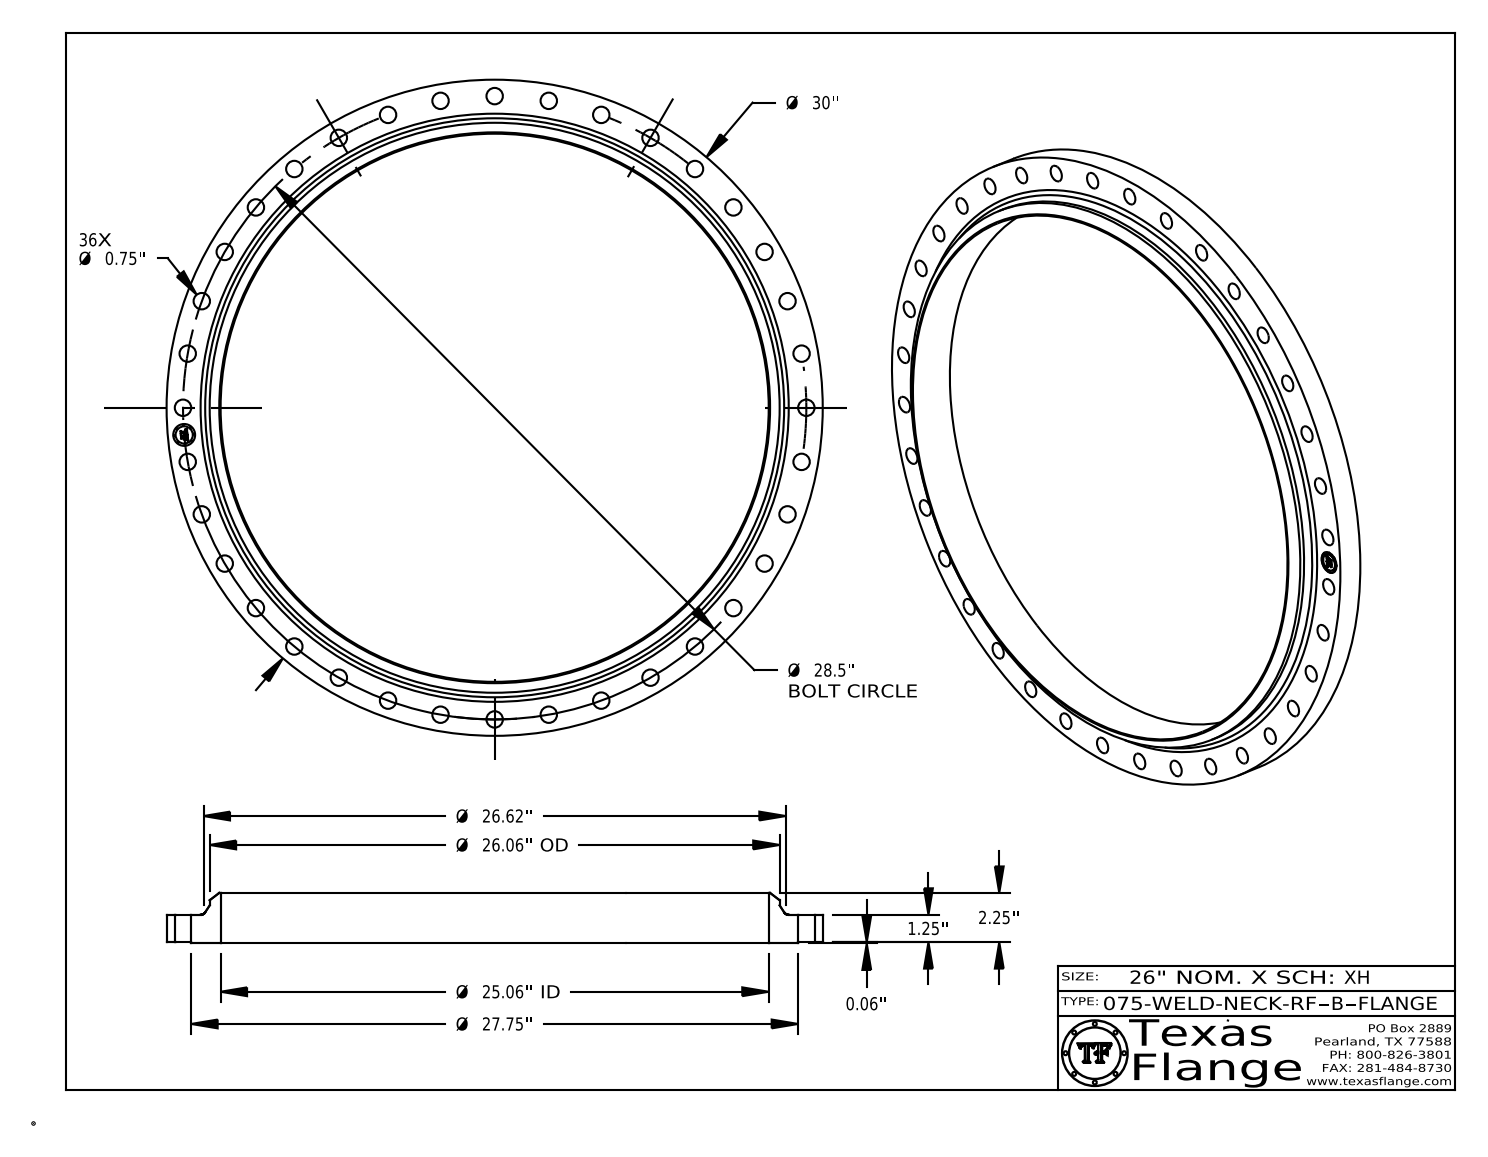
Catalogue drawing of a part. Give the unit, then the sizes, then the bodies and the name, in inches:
Units: inches
Overall size (bounding box): 30 × 30 × 2.313
Round holes (diameter × count): ⌀0.75 ×36, ⌀1 ×1, ⌀25.06 ×1
Round bosses / shafts (diameter × count): ⌀0.061 ×8, ⌀30 ×1, ⌀27.75 ×1, ⌀26.06 ×1, ⌀0.788 ×1
Main face-to-face distances: 1.313, 0.063, 1.25, 2.313, 2.25, 1, 0.015, 1.298, 1.235, 1.015
Hole centre spacings: 14.25, 25.83, 9.748, 21.832, 12.044, 2.484, 24.682, 16.347
Volume: 293.6 in³ · Surface area: 852.9 in²
Bodies: 1 solid, 475 faces (369 planar, 100 cylindrical, 6 other)
Part name (STEP PRODUCT): 075-WELD-NECK-RF, Series B
STEP written by: CATIA V5 STEP AP214 (AUTOMOTIVE_DESIGN)
